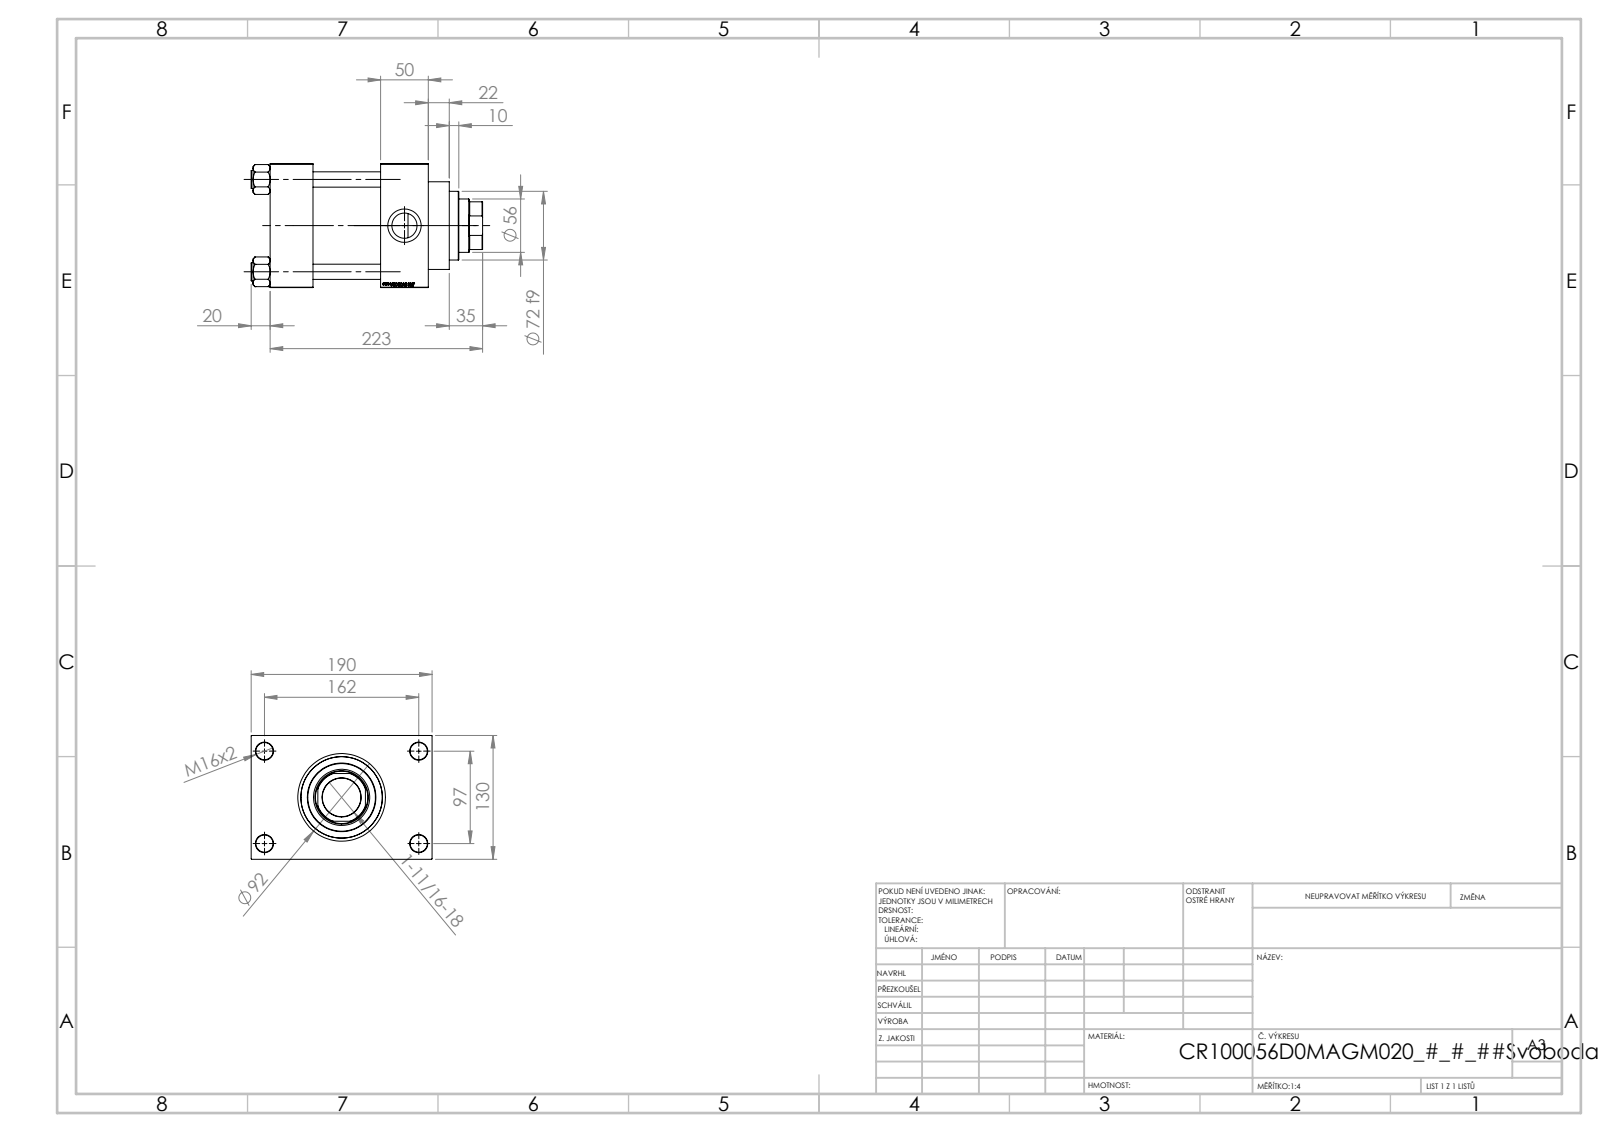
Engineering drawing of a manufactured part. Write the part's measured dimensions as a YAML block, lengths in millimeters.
part_name: "NUT_M5_D; V215CR_D_Body; V215CR_VCP_D; V215_VC_A (+1 more)"
step_written_by: "SolidWorks 2019 (CONFIG_CONTROL_DESIGN)"
units: millimeters
bodies: {solids: 11, faces: 1152, planar: 545, cylindrical: 89, other: 518}
overall_size: [243, 190, 130]
volume: 2628000
surface_area: 362372
round_holes:
  - {diameter: 16, count: 4}
  - {diameter: 18, count: 4}
  - {diameter: 7, count: 2}
  - {diameter: 26.44, count: 2}
  - {diameter: 35, count: 2}
  - {diameter: 40.5, count: 1}
  - {diameter: 56, count: 1}
  - {diameter: 59, count: 1}
  - {diameter: 76, count: 1}
  - {diameter: 85.5, count: 1}
  - {diameter: 100, count: 1}
round_bosses_or_shafts:
  - {diameter: 19, count: 4}
  - {diameter: 106, count: 1}
  - {diameter: 92, count: 1}
  - {diameter: 72, count: 1}
partial_cylinders:
  - {radius: 27, count: 1}
face_to_face_distances: [130, 116, 50, 45, 71, 166, 121, 160, 30, 20]
hole_center_spacings: [32.55, 68.52, 94.41, 96.9, 102.27, 129.45, 161.73, 97]
